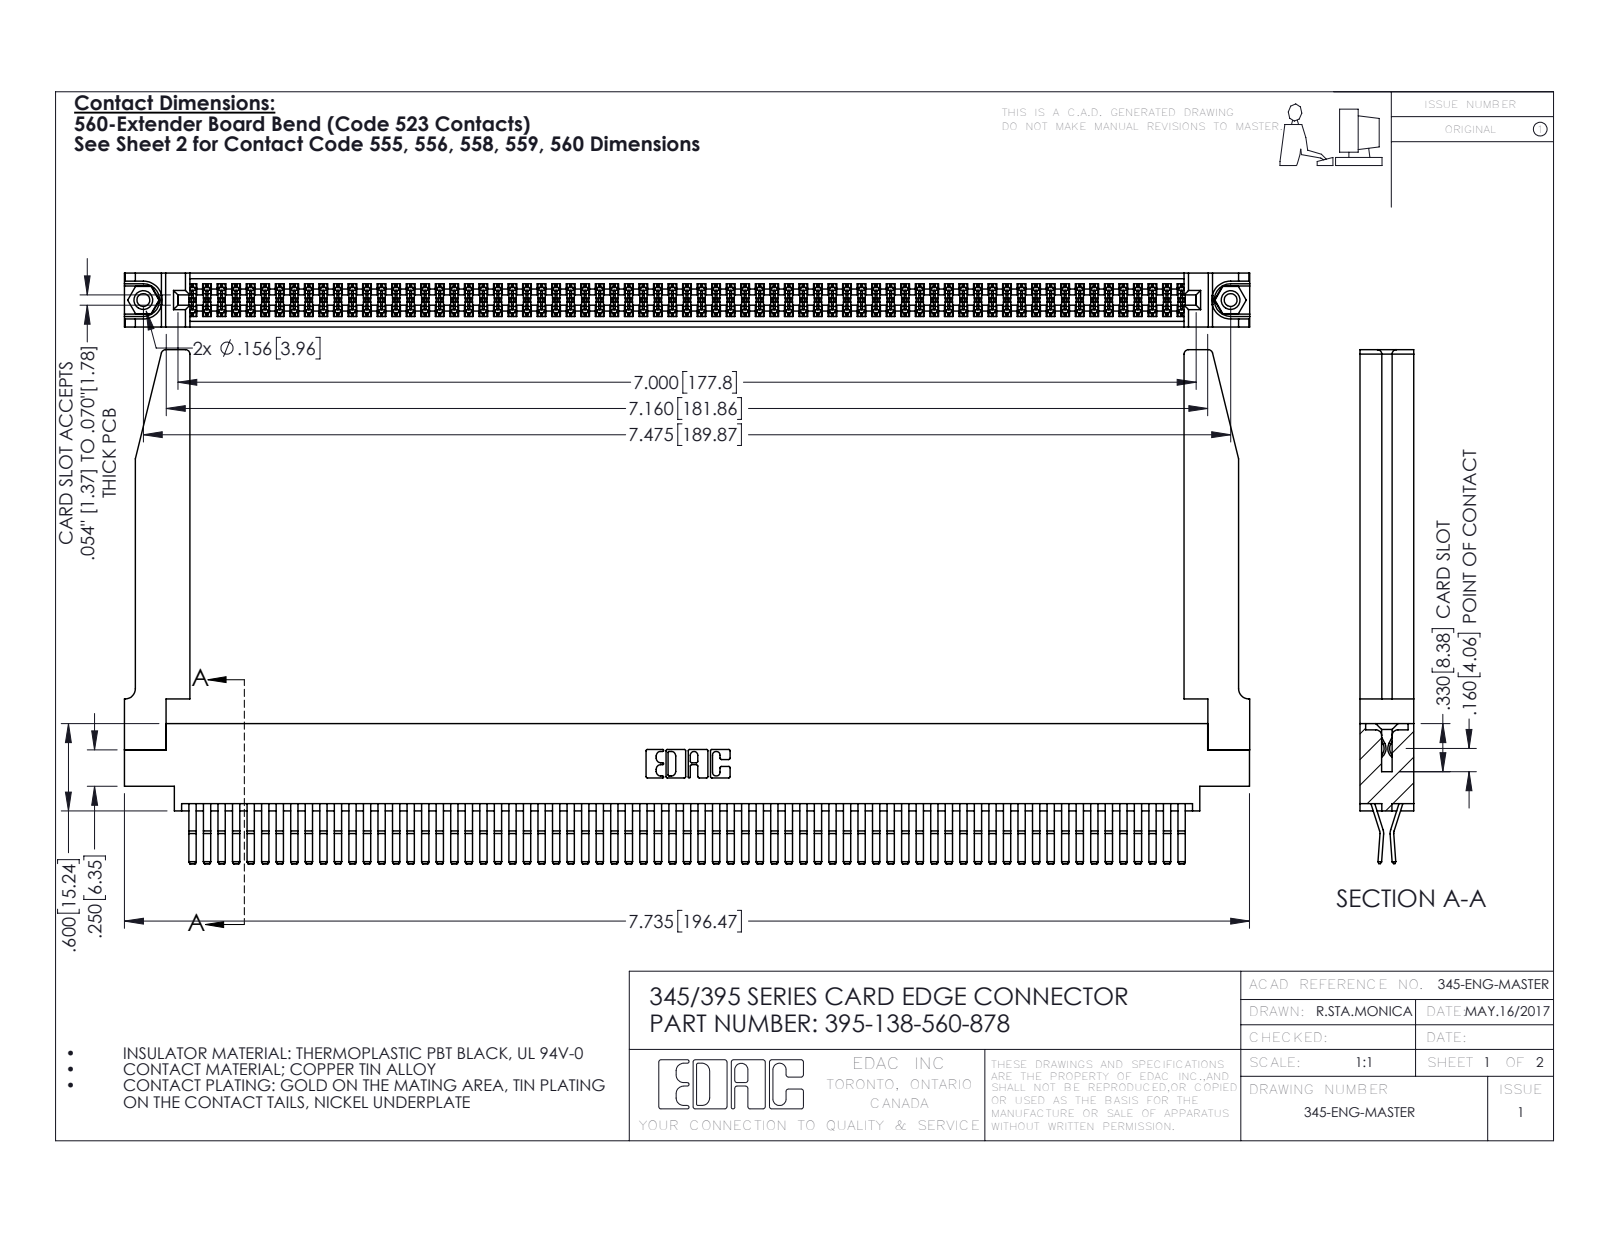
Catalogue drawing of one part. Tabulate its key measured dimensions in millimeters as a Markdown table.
| quantity | value |
| --- | --- |
| part name | 345-292-001_560 Tail; 345-250-001_345-250-001-102; 395-138-560-878; 345-220-078_345-220-078 (+1 more) |
| STEP written by | SolidWorks 2016 (CONFIG_CONTROL_DESIGN) |
| units | millimeters |
| bodies | 143 solids, 7540 faces (4780 planar, 2708 cylindrical, 52 other) |
| overall size | 196.5 × 89.7 × 9.4 |
| volume | 27 910 mm³ |
| surface area | 39 590 mm² |
| round holes (diameter × count) | 2.3 × 2, 3.2 × 2, 4 × 2, 1.6 × 1 |
| round bosses / shafts (diameter × count) | 3.9 × 2 |
| partial cylindrical surfaces (radius × count) | 0.2 × 207, 0.3 × 22, 0.8 × 8, 0.2 × 6, 0.8 × 6, 0.7 × 3, 0.3 × 2, 0.4 × 2 |
| main face-to-face distances | 1.8, 9.4, 0.6, 7.6, 2.5, 6.9, 5.1, 5.7, 4.4, 3.8 |
| hole center spacings | 6.9, 183.9, 189.9 |
